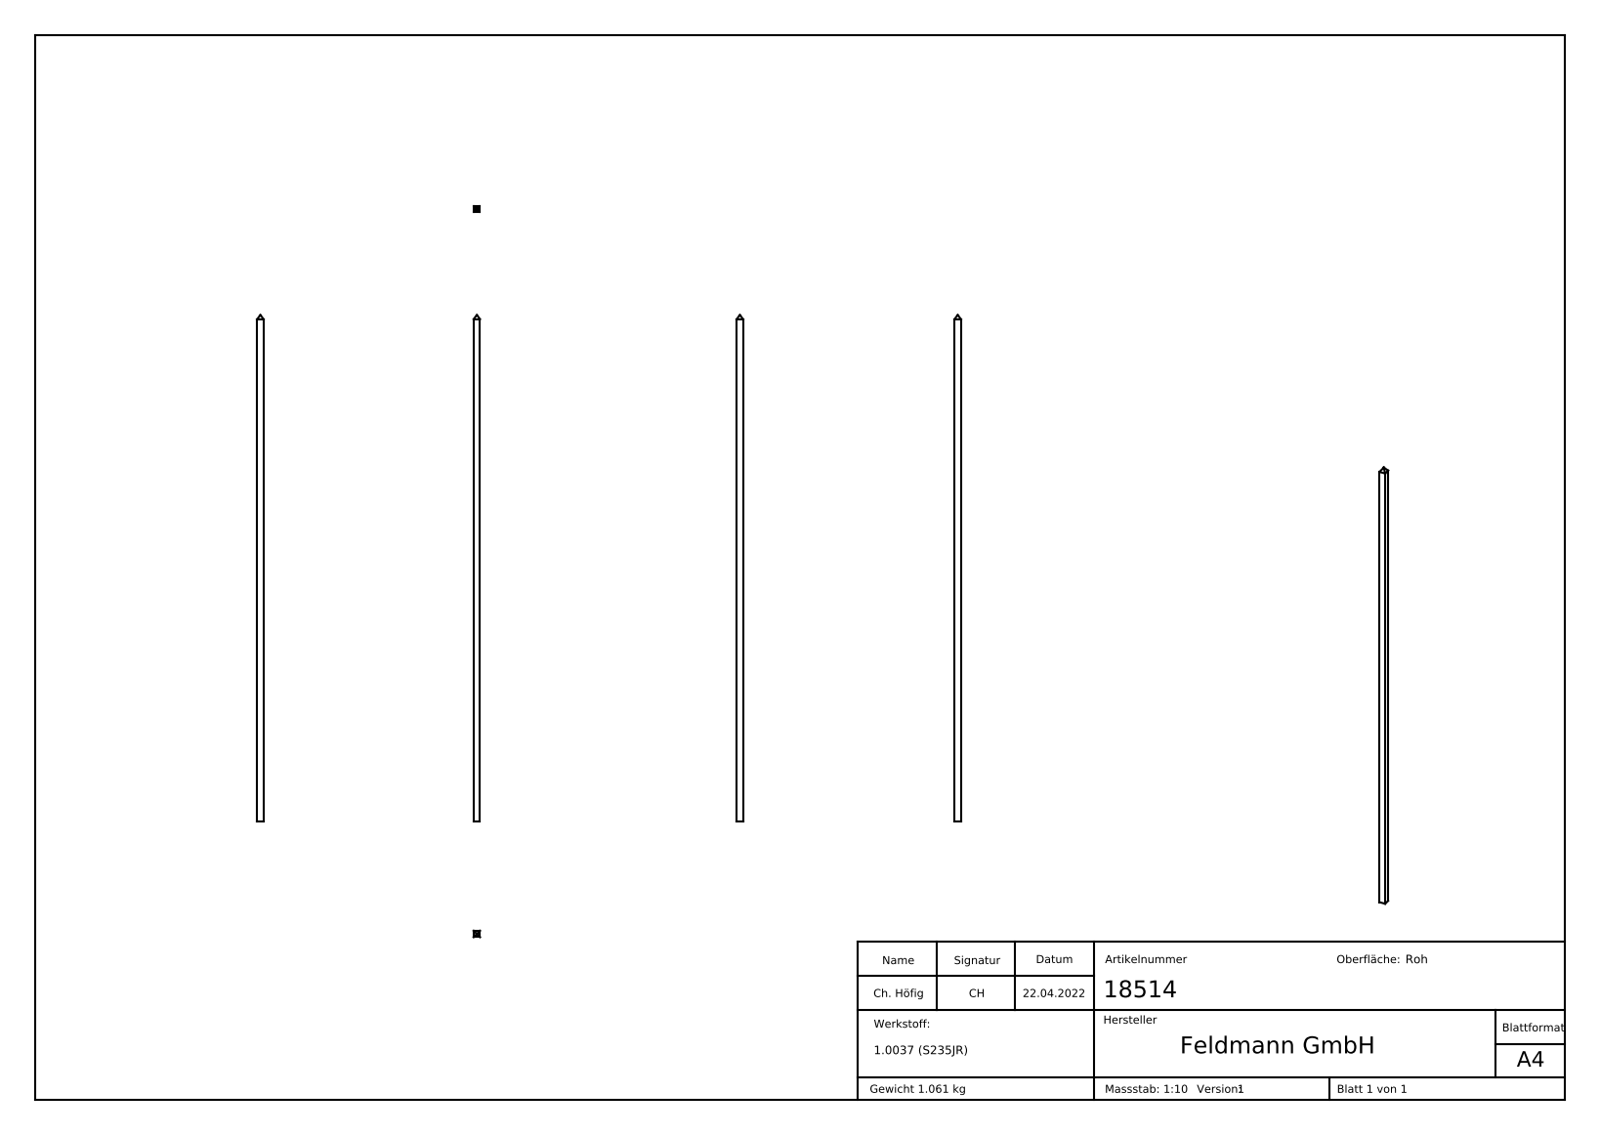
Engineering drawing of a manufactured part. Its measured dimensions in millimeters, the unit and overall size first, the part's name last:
Units: millimetres
Overall size (bounding box): 950 × 12 × 12
Main face-to-face distances: 12, 1.87, 7.25, 4.75, 0.34, 3.15, 0.32, 1.32, 1.83, 1.94
Volume: 136 060 mm³ · Surface area: 45 617 mm²
Bodies: 1 solid, 230 faces (137 planar, 0 cylindrical, 93 other)
Part name (STEP PRODUCT): 18514
STEP written by: SolidWorks 2018 (CONFIG_CONTROL_DESIGN)
